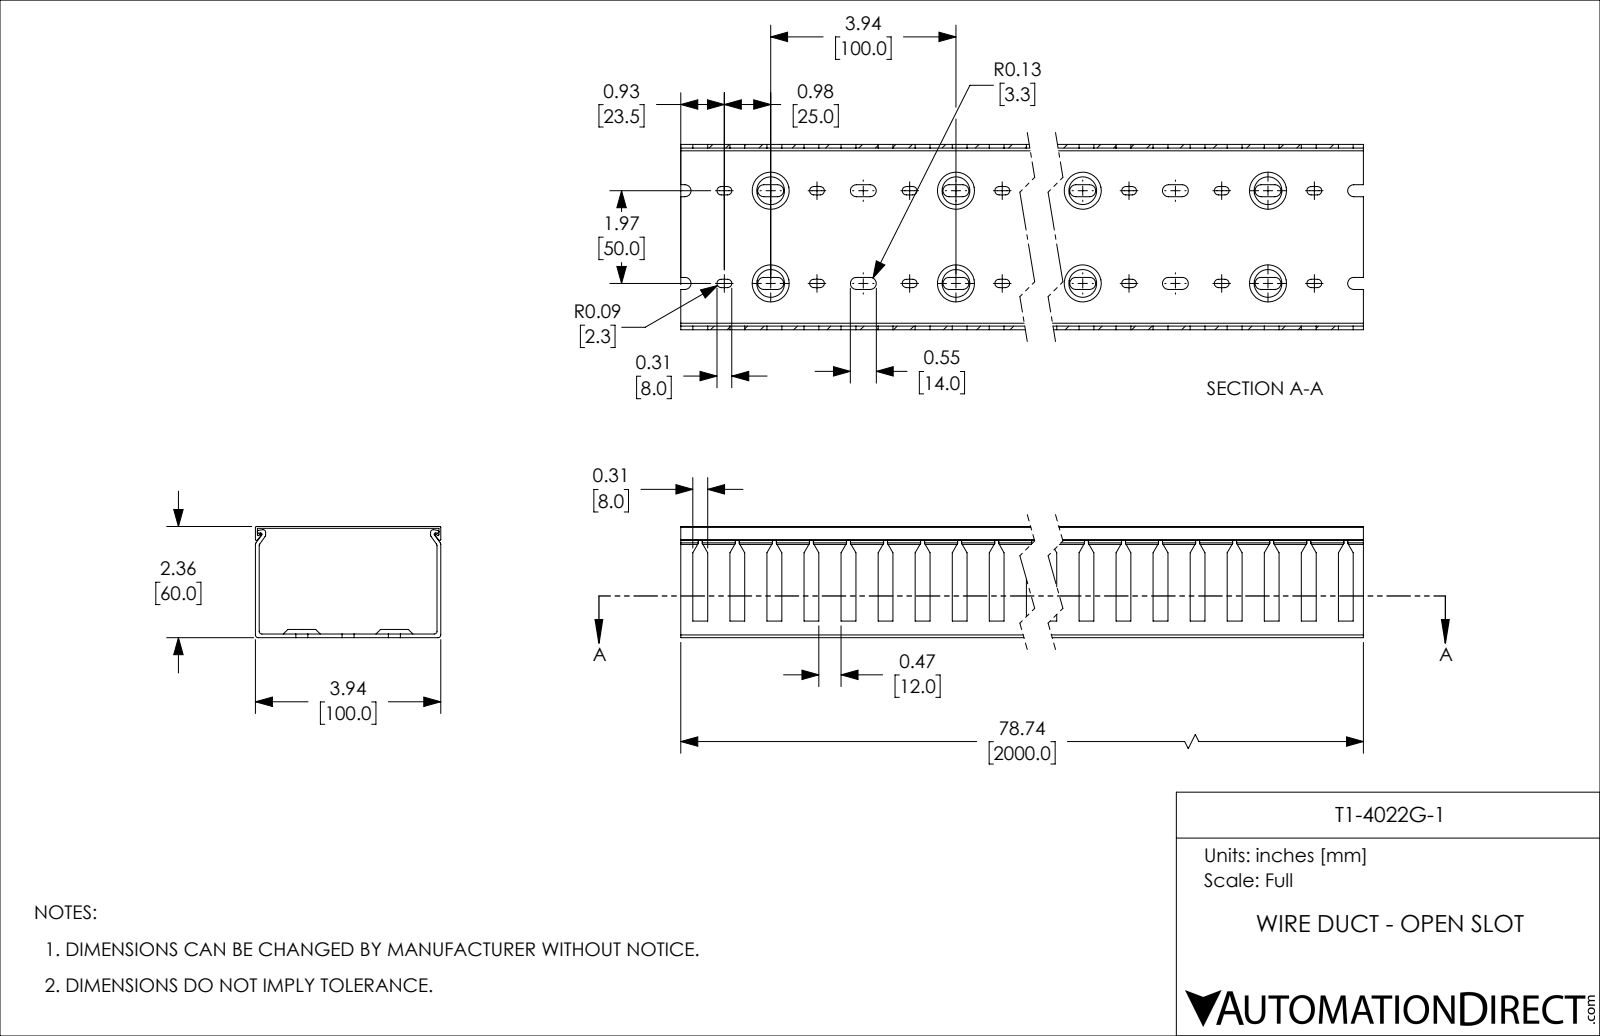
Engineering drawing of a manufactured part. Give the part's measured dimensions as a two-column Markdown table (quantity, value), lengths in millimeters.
| quantity | value |
| --- | --- |
| part name | T1-4022G-1 |
| STEP written by | SolidWorks 2021 (CONFIG_CONTROL_DESIGN) |
| units | millimeters |
| bodies | 2 solids, 1573 faces (762 planar, 731 cylindrical, 80 other) |
| overall size | 2000 × 100 × 60 |
| volume | 1 090 000 mm³ |
| surface area | 1 328 000 mm² |
| partial cylindrical surfaces (radius × count) | 3.25 × 200, 2.25 × 160, 1.5 × 12, 0.5 × 8, 0.75 × 6 |
| main face-to-face distances | 2, 1, 60, 98, 59, 57, 58, 100, 96, 99 |
